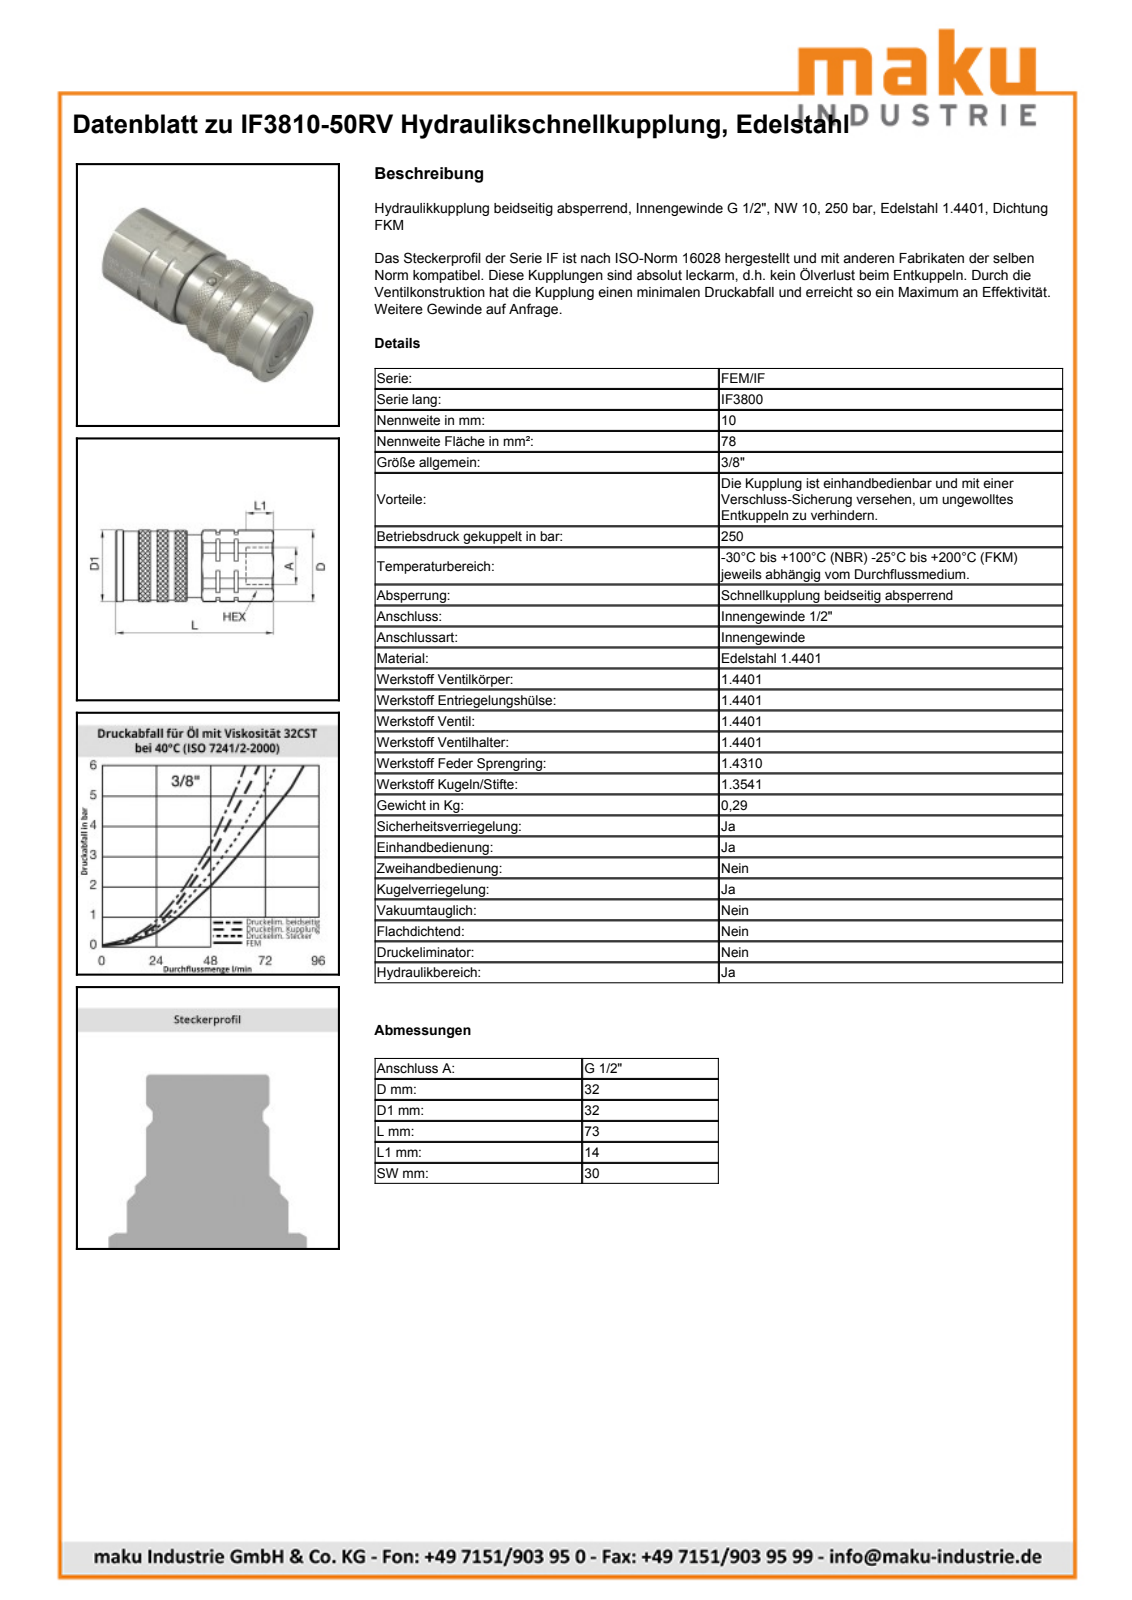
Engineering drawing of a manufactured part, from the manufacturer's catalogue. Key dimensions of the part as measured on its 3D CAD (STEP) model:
Part name (STEP PRODUCT): IF3810-50RV
STEP written by: SolidWorks 2009 (AUTOMOTIVE_DESIGN)
Units: millimetres
Bodies: 1 solid, 167 faces (54 planar, 69 cylindrical, 44 other)
Overall size (bounding box): 72.5 × 32 × 32
Volume: 49 450 mm³ · Surface area: 11 622 mm²
Round holes (diameter × count): ⌀2 ×1, ⌀12.65 ×1, ⌀18.63 ×1, ⌀19.85 ×1, ⌀24.5 ×1, ⌀28.2 ×1
Round bosses / shafts (diameter × count): ⌀32 ×1, ⌀30.8 ×1, ⌀28 ×1, ⌀24.3 ×1, ⌀19.75 ×1, ⌀12.5 ×1
Partial cylindrical surfaces — rounded edges, fillets, slot ends (radius × count): R0.5 ×2, R12.39 ×1, R15.15 ×1
Main face-to-face distances: 30, 72.5, 72, 0.5, 17.53, 54.47, 54.97, 8, 34, 16.47
